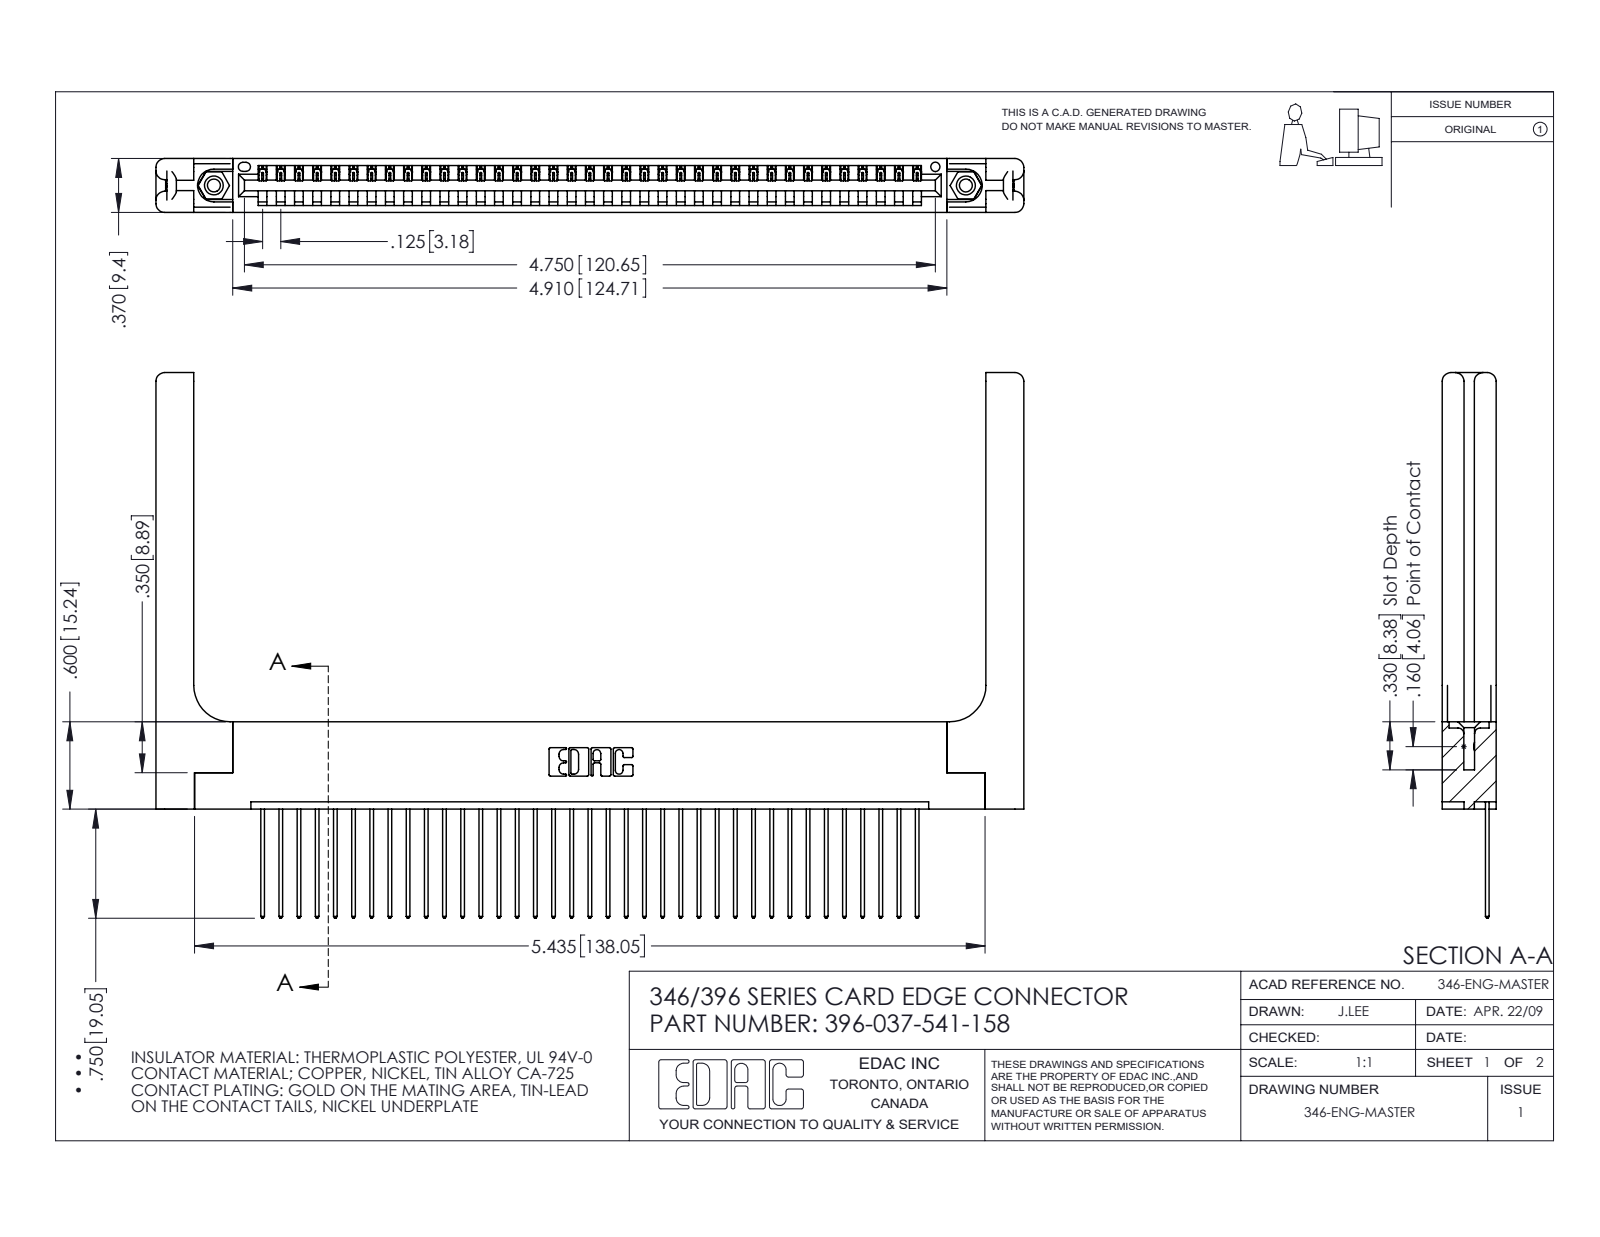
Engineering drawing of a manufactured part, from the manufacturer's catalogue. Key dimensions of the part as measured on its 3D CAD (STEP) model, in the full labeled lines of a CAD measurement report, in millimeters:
Part name (STEP PRODUCT): 346 Part_Flush Mounting Lugs - 0.156 Dia-TH; 345-292-001_345-293-141; 346-220-058_345-220-058; 345-250-001_345-250-001-102 (+1 more)
STEP written by: SolidWorks 2016 (CONFIG_CONTROL_DESIGN)
Units: millimetres
Bodies: 42 solids, 2524 faces (1704 planar, 760 cylindrical, 60 other)
Overall size (bounding box): 151.5 × 95.3 × 9.4
Volume: 22 110 mm³ · Surface area: 24 080 mm²
Round holes (diameter × count): ⌀2.3 ×2, ⌀3.2 ×2, ⌀4 ×2, ⌀1.6 ×1
Round bosses / shafts (diameter × count): ⌀3.9 ×2
Partial cylindrical surfaces — rounded edges, fillets, slot ends (radius × count): R0.2 ×74, R0.3 ×74, R0.3 ×22, R1.5 ×16, R0.2 ×6, R0.8 ×6, R0.7 ×3, R0.8 ×2
Main face-to-face distances: 9.4, 1.2, 8.2, 1.8, 3.8, 3.8, 6.4, 7.6, 0.6, 5.6
Hole centre spacings: 6.2, 126, 131.3
